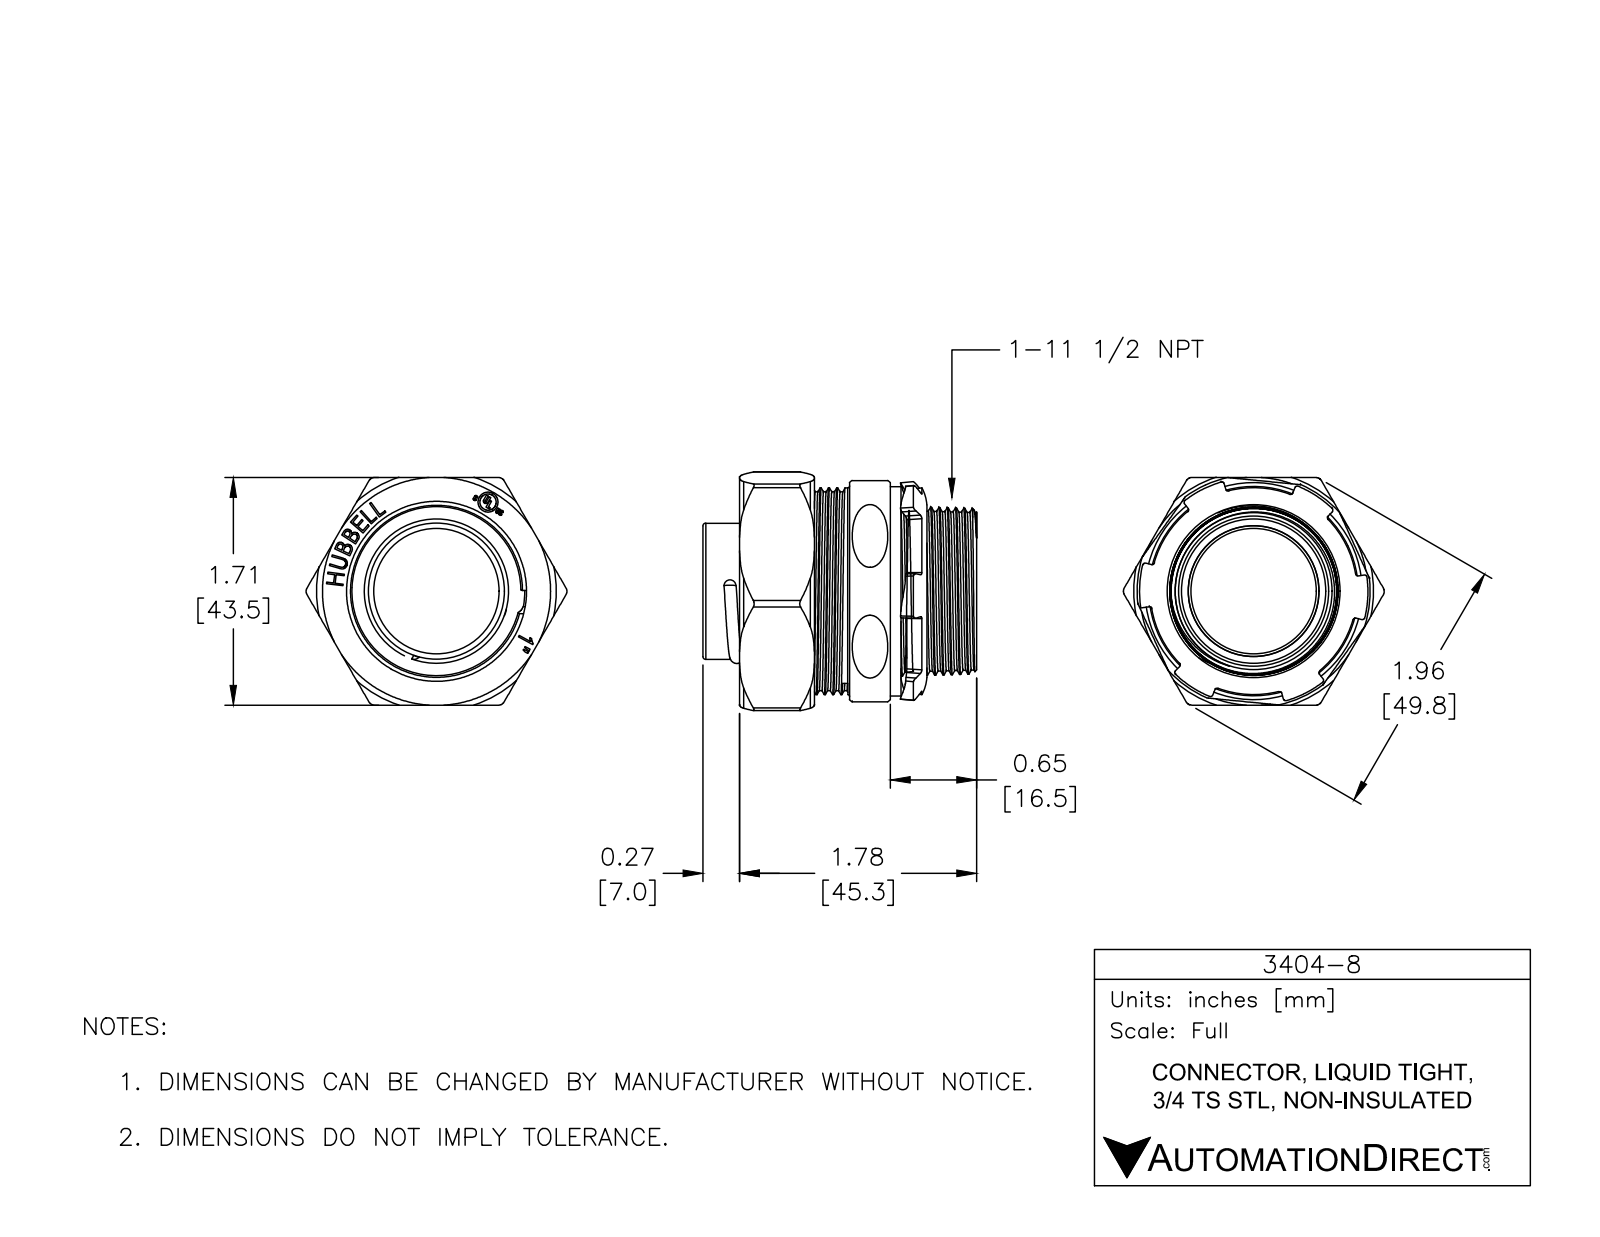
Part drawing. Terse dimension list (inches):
name: 3404 SEAL_1; 3404 FERRULE_installed; 3404 COMPRESSION NUT HEX_1; 3404 LOCK NUT (+3 more)
written by: SolidWorks 2014 (AUTOMOTIVE_DESIGN)
unit: in
bodies: 6 solids, 485 faces (183 planar, 97 cylindrical, 205 other)
size: 2.059 × 1.954 × 1.795
volume: 1.098 in³; area: 46.25 in²
holes: 1× ⌀0.15, 1× ⌀0.943, 1× ⌀0.985, 1× ⌀1.215, 1× ⌀1.331, 1× ⌀1.335, 1× ⌀1.354, 1× ⌀1.395, 1× ⌀1.516
bosses: 1× ⌀1.575, 1× ⌀1.555, 1× ⌀1.496, 1× ⌀1.37, 1× ⌀1.024, 1× ⌀0.983, 1× ⌀0.122
rounds: 8× R0.01, 6× R0.05, 2× R0.046, 1× R0.005, 1× R0.013, 1× R0.019
face distances: 1.135, 1.214, 0.079, 0.08, 1.055, 0.159, 1.713, 1.713, 1.712, 1.665
hole spacings: 0.775
